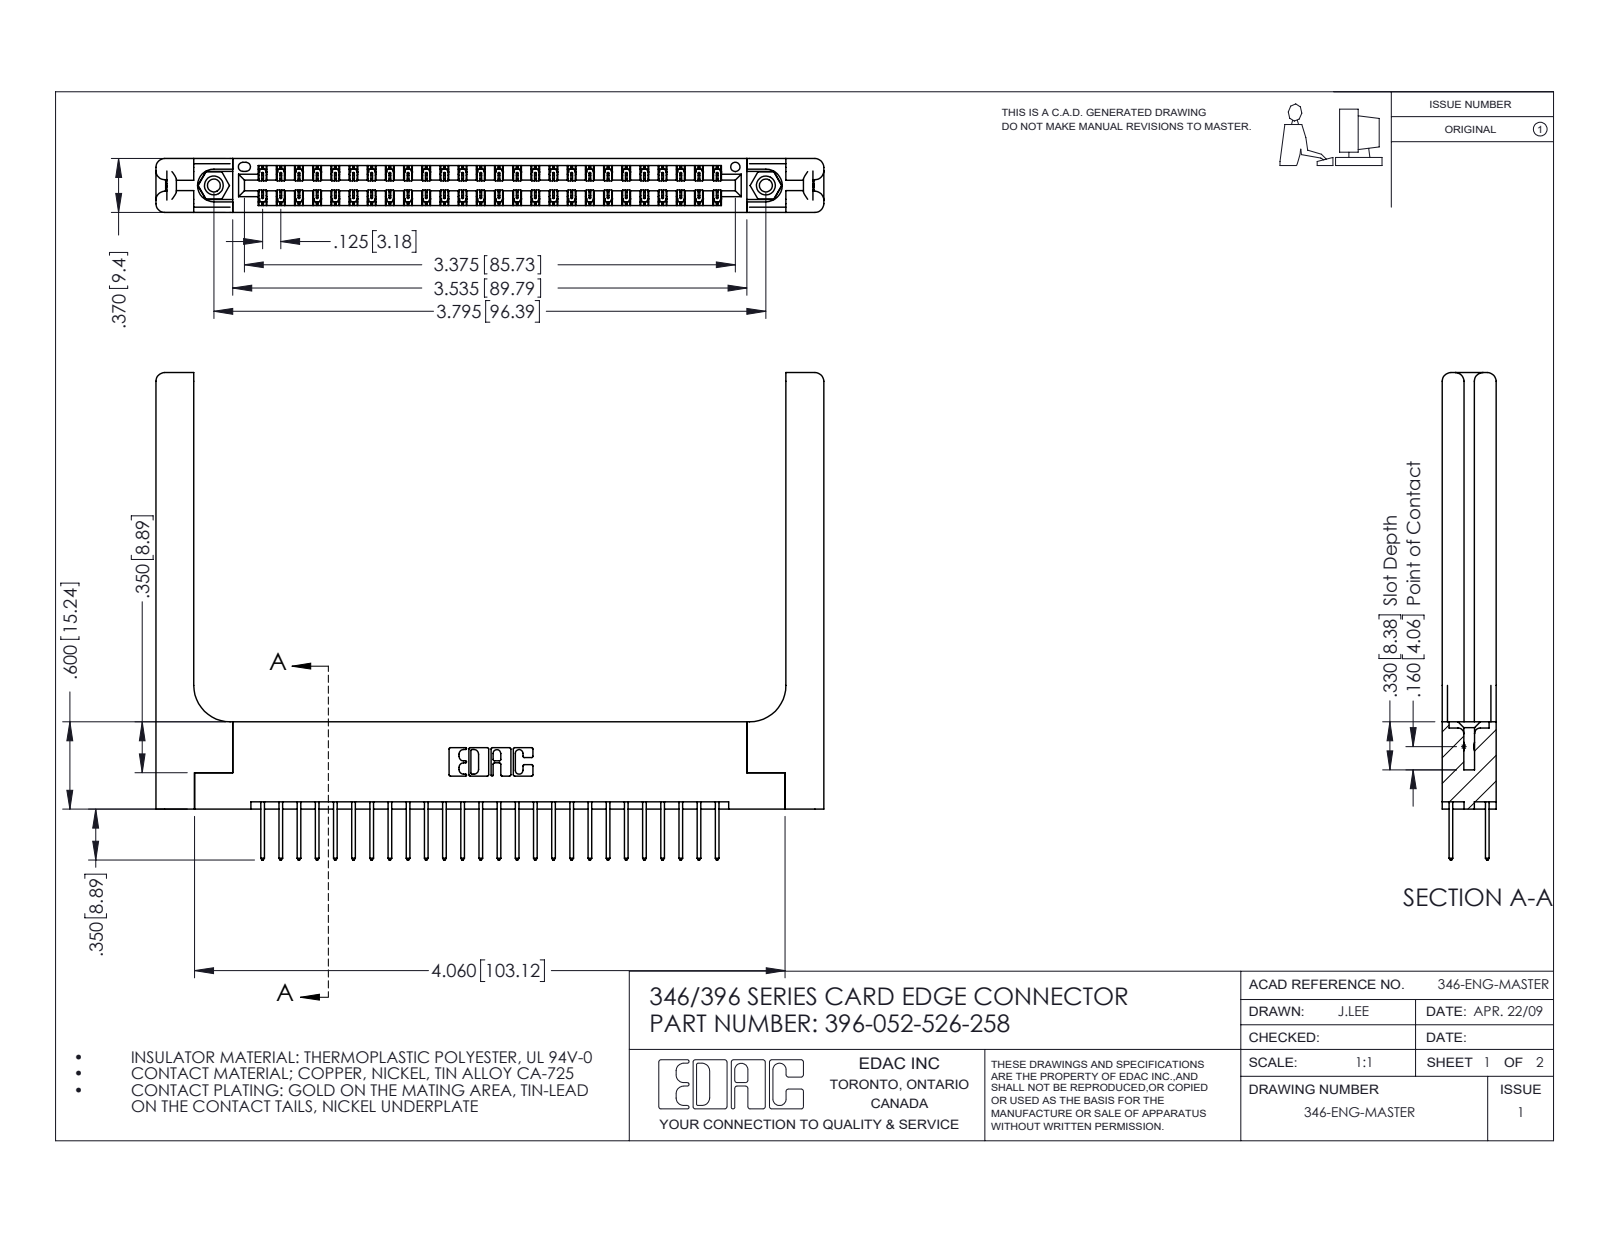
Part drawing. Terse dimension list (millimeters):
name: 345-250-001_345-250-001-102; 346 Part_Flush Mounting Lugs - 0.156 Dia-TH; 396-052-526-258; 346-220-058_345-220-058 (+1 more)
written by: SolidWorks 2016 (CONFIG_CONTROL_DESIGN)
unit: mm
bodies: 57 solids, 3082 faces (2044 planar, 978 cylindrical, 60 other)
size: 116.6 × 85.1 × 9.4
volume: 18 830 mm³; area: 20 680 mm²
holes: 2× ⌀2.3, 2× ⌀3.2, 2× ⌀4, 1× ⌀1.6
bosses: 2× ⌀3.9
rounds: 78× R0.2, 52× R0.3, 22× R0.3, 16× R1.5, 6× R0.2, 6× R0.8, 3× R0.7, 2× R0.4
face distances: 9.4, 1.8, 1.2, 8.2, 6.4, 3.8, 3.8, 0.6, 7.6, 7
hole spacings: 6.2, 91.1, 96.4
